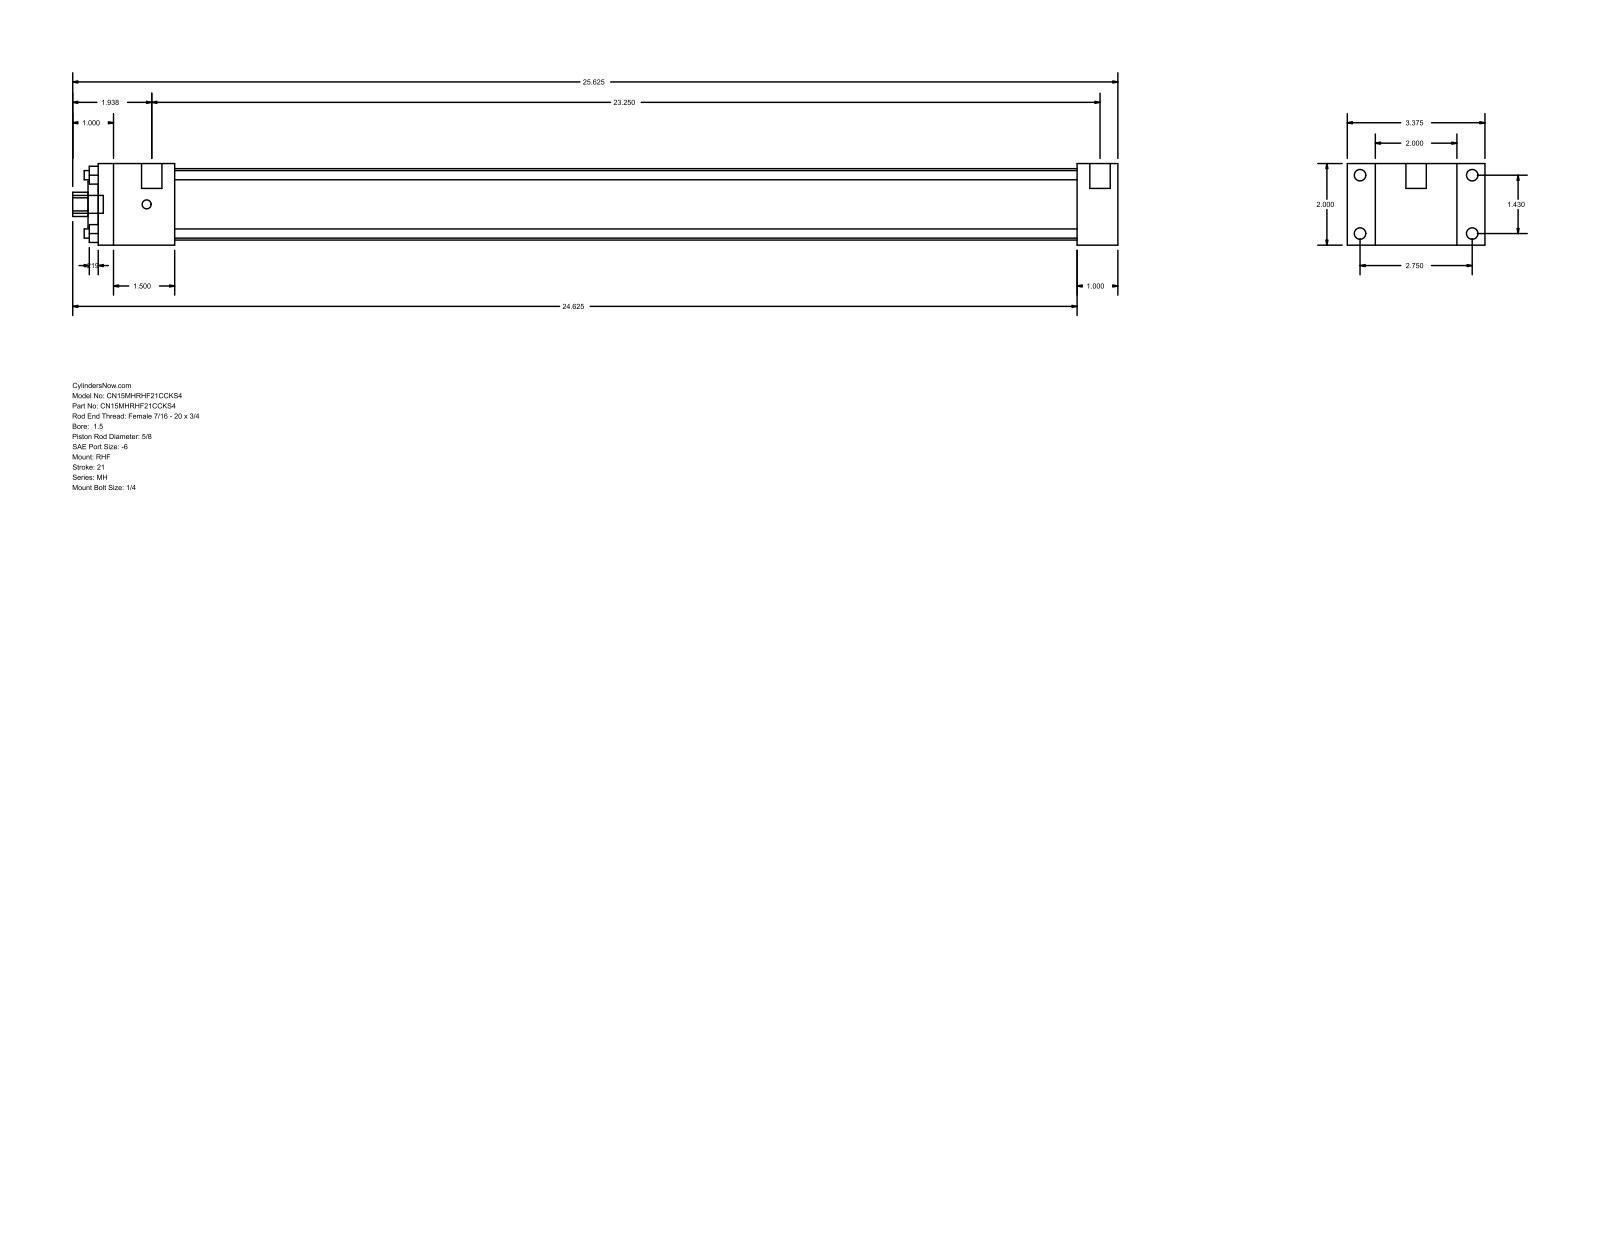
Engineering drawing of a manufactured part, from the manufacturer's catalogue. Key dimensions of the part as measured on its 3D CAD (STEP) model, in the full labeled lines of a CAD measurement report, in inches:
Part name (STEP PRODUCT): MH_RHF__0150_0.625
STEP written by: GSSL Pune (CONFIG_CONTROL_DESIGN)
Units: inches
Bodies: 0 solids, 88 faces (60 planar, 28 cylindrical, 0 other)
Overall size (bounding box): 25.625 × 3.375 × 2
Round holes (diameter × count): ⌀0.225 ×4, ⌀0.625 ×1, ⌀1.125 ×1, ⌀1.75 ×1
Round bosses / shafts (diameter × count): ⌀0.281 ×4, ⌀0.219 ×4, ⌀0.5 ×2, ⌀0.437 ×1
Partial cylindrical surfaces — rounded edges, fillets, slot ends (radius × count): R0.297 ×1
Main face-to-face distances: 2, 0.687, 2.687, 1, 24, 25, 3.375, 1.875, 22.125, 23.125
Hole centre spacings: 1.011, 1.43, 2.022
